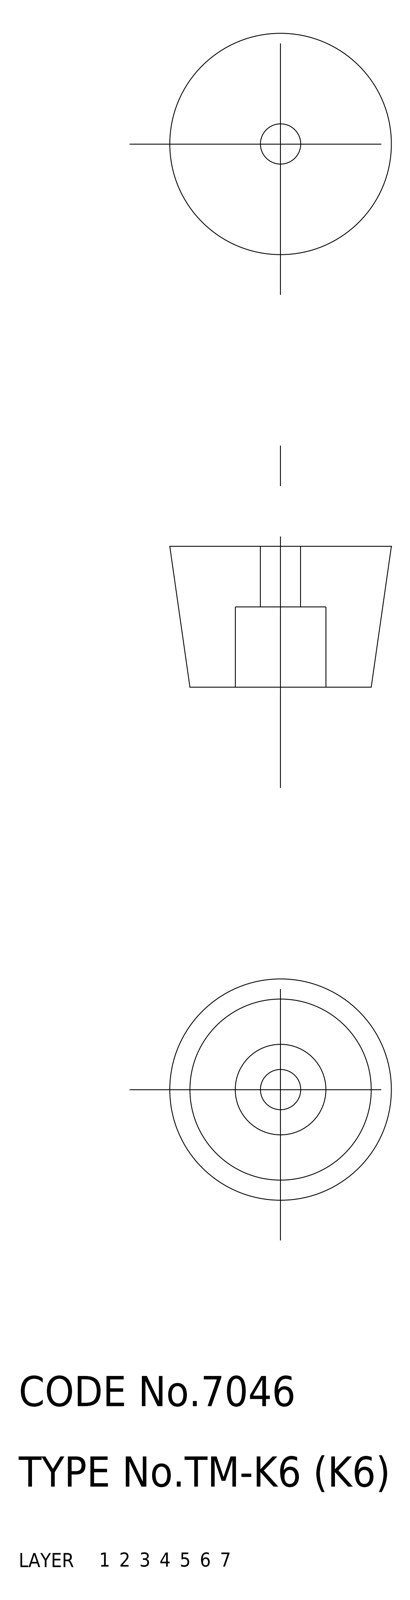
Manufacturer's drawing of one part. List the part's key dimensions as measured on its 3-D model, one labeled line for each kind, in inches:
Part name (STEP PRODUCT): rubber foot
STEP written by: CADfix (AUTOMOTIVE_DESIGN)
Units: inches
Bodies: 1 solid, 9 faces (0 planar, 0 cylindrical, 9 other)
Overall size (bounding box): 0.866 × 0.866 × 0.551
Volume: 0.234 in³ · Surface area: 2.792 in²
